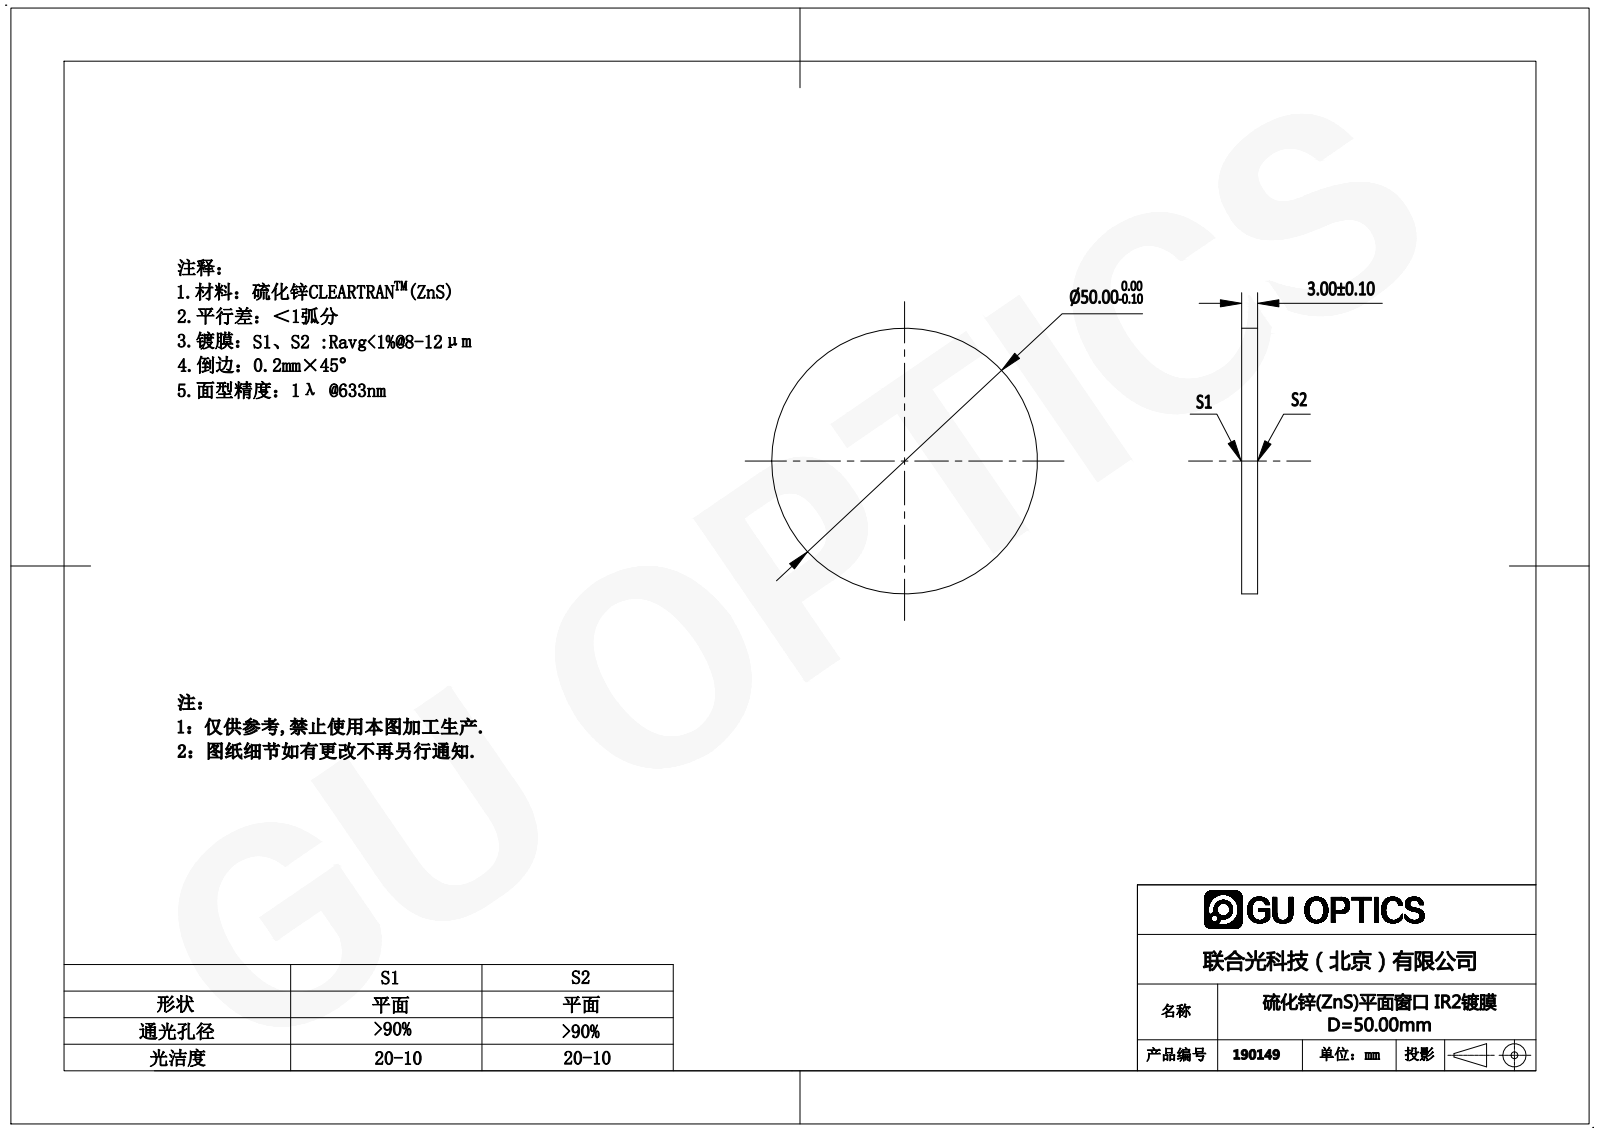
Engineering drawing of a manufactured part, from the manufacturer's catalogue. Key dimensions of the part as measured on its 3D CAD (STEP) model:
Part name (STEP PRODUCT): 190148
STEP written by: SolidWorks 2016 (AUTOMOTIVE_DESIGN)
Units: millimetres
Bodies: 1 solid, 4 faces (2 planar, 2 cylindrical, 0 other)
Overall size (bounding box): 50 × 50 × 3
Volume: 5 890 mm³ · Surface area: 4 398 mm²
Round bosses / shafts (diameter × count): ⌀50 ×1
Main face-to-face distances: 3
